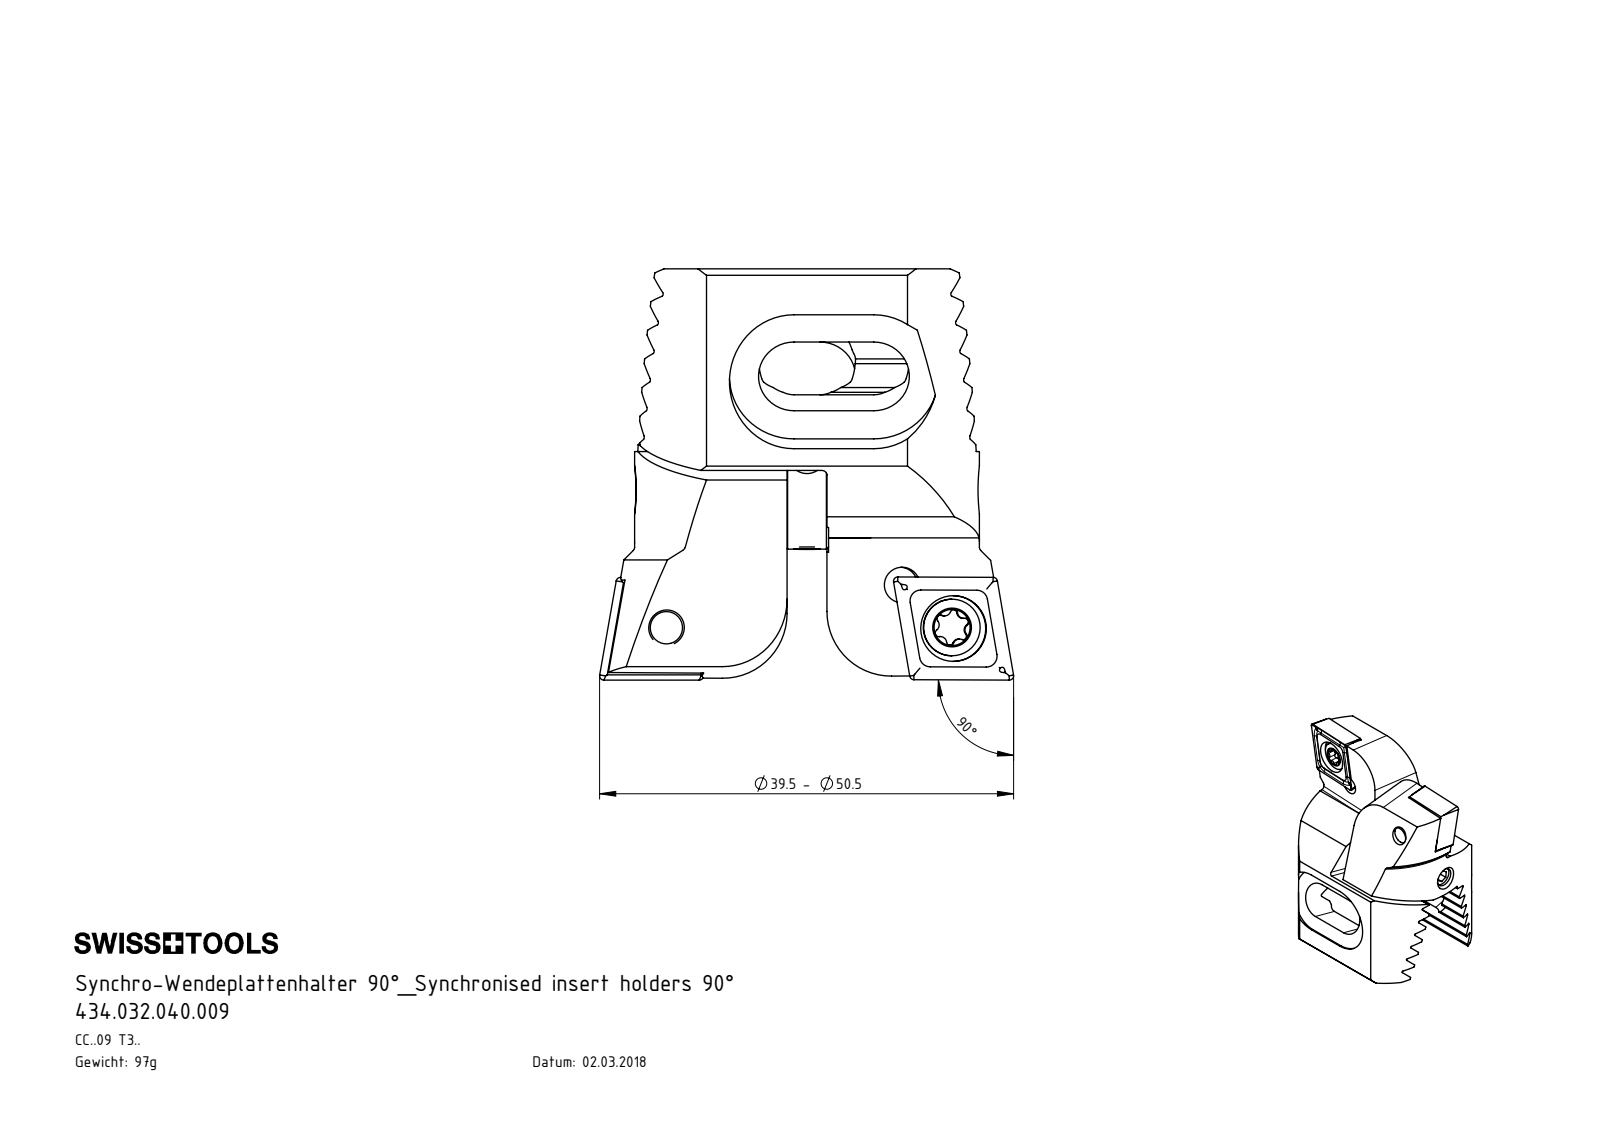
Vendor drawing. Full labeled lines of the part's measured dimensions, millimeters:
Part name (STEP PRODUCT): CCMT09T304; ISO 4026 - M3 x 3; Z32.WCB.B12.021; WCB-ER2.001.009_A (+4 more)
STEP written by: SolidWorks 2017 (AUTOMOTIVE_DESIGN)
Units: millimetres
Bodies: 11 solids, 401 faces (193 planar, 102 cylindrical, 106 other)
Overall size (bounding box): 38.42 × 38.15 × 26.2
Volume: 12 355 mm³ · Surface area: 8 863 mm²
Round holes (diameter × count): ⌀3.3 ×4, ⌀1 ×3, ⌀2.5 ×3, ⌀4.4 ×2, ⌀6.1 ×2, ⌀3.5 ×1
Round bosses / shafts (diameter × count): ⌀3 ×4, ⌀4 ×3, ⌀5.25 ×2, ⌀11 ×1
Partial cylindrical surfaces — rounded edges, fillets, slot ends (radius × count): R0.2 ×12, R0.34 ×12, R0.59 ×12, R1 ×8, R6 ×6, R0.5 ×4, R3.3 ×4, R16 ×2
Main face-to-face distances: 2.38, 9.53, 7.15, 4.76, 11.91, 3.85, 4.77, 0.81, 4.09, 9.62
Hole centre spacings: 10, 27.07, 2, 6.09, 6.1, 6.25, 6.26, 10.21
